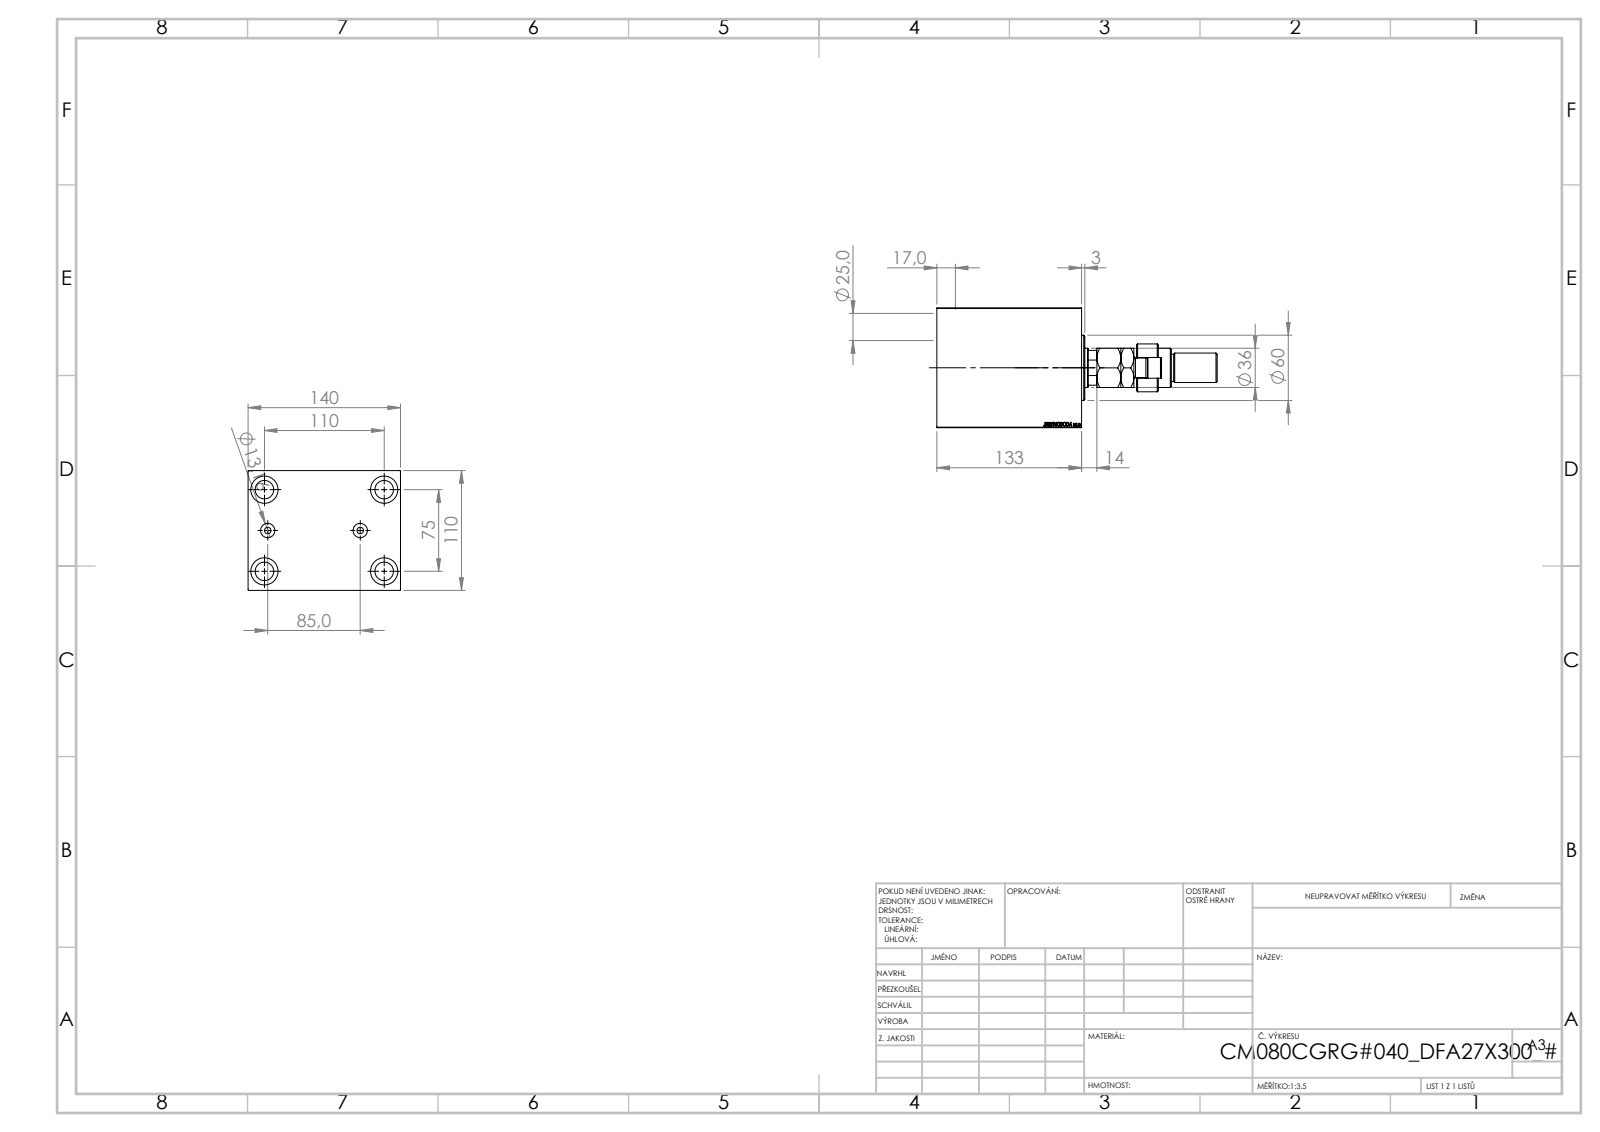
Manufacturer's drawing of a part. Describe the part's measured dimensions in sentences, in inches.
The part is named "V450CM_C_VCP; MFA; V450CM_VC_B; FEMALE_PART_FOR_DFA (+1 more)". Its 3-D file was written by "SolidWorks 2019 (CONFIG_CONTROL_DESIGN)". It is 5 solids with 948 faces: 439 planar, 71 cylindrical and 438 other. Overall it measures 10.138 by 5.512 by 4.331 inches. Its volume is 111.1 cubic inches and its surface area 363.8 square inches. Round holes: 4 of diameter 0.669, 4 of diameter 0.984, 2 of diameter 0.236, 2 of diameter 0.518, 1 of diameter 1.004, 1 of diameter 1.555, 1 of diameter 3.15, 1 of diameter 3.228, 1 of diameter 3.425. Round bosses or shafts: 1 of diameter 2.362, 1 of diameter 1.732, 1 of diameter 1.417, 1 of diameter 1.102, 1 of diameter 1.063, 1 of diameter 0.984, 1 of diameter 0.709. Partial cylindrical surfaces (rounded edges, fillets, slot ends): 1 of radius 0.374, 1 of radius 0.591, 1 of radius 0.689. The main face-to-face distances are 4.331, 5.512, 5.236, 4.272, 0.965, 1.469, 2.803, 3.768, 3.043, 1.575. The hole center spacings are 1.556, 2.621, 4.113, 1.673, 2.953, 4.331, 5.242, 3.346.
